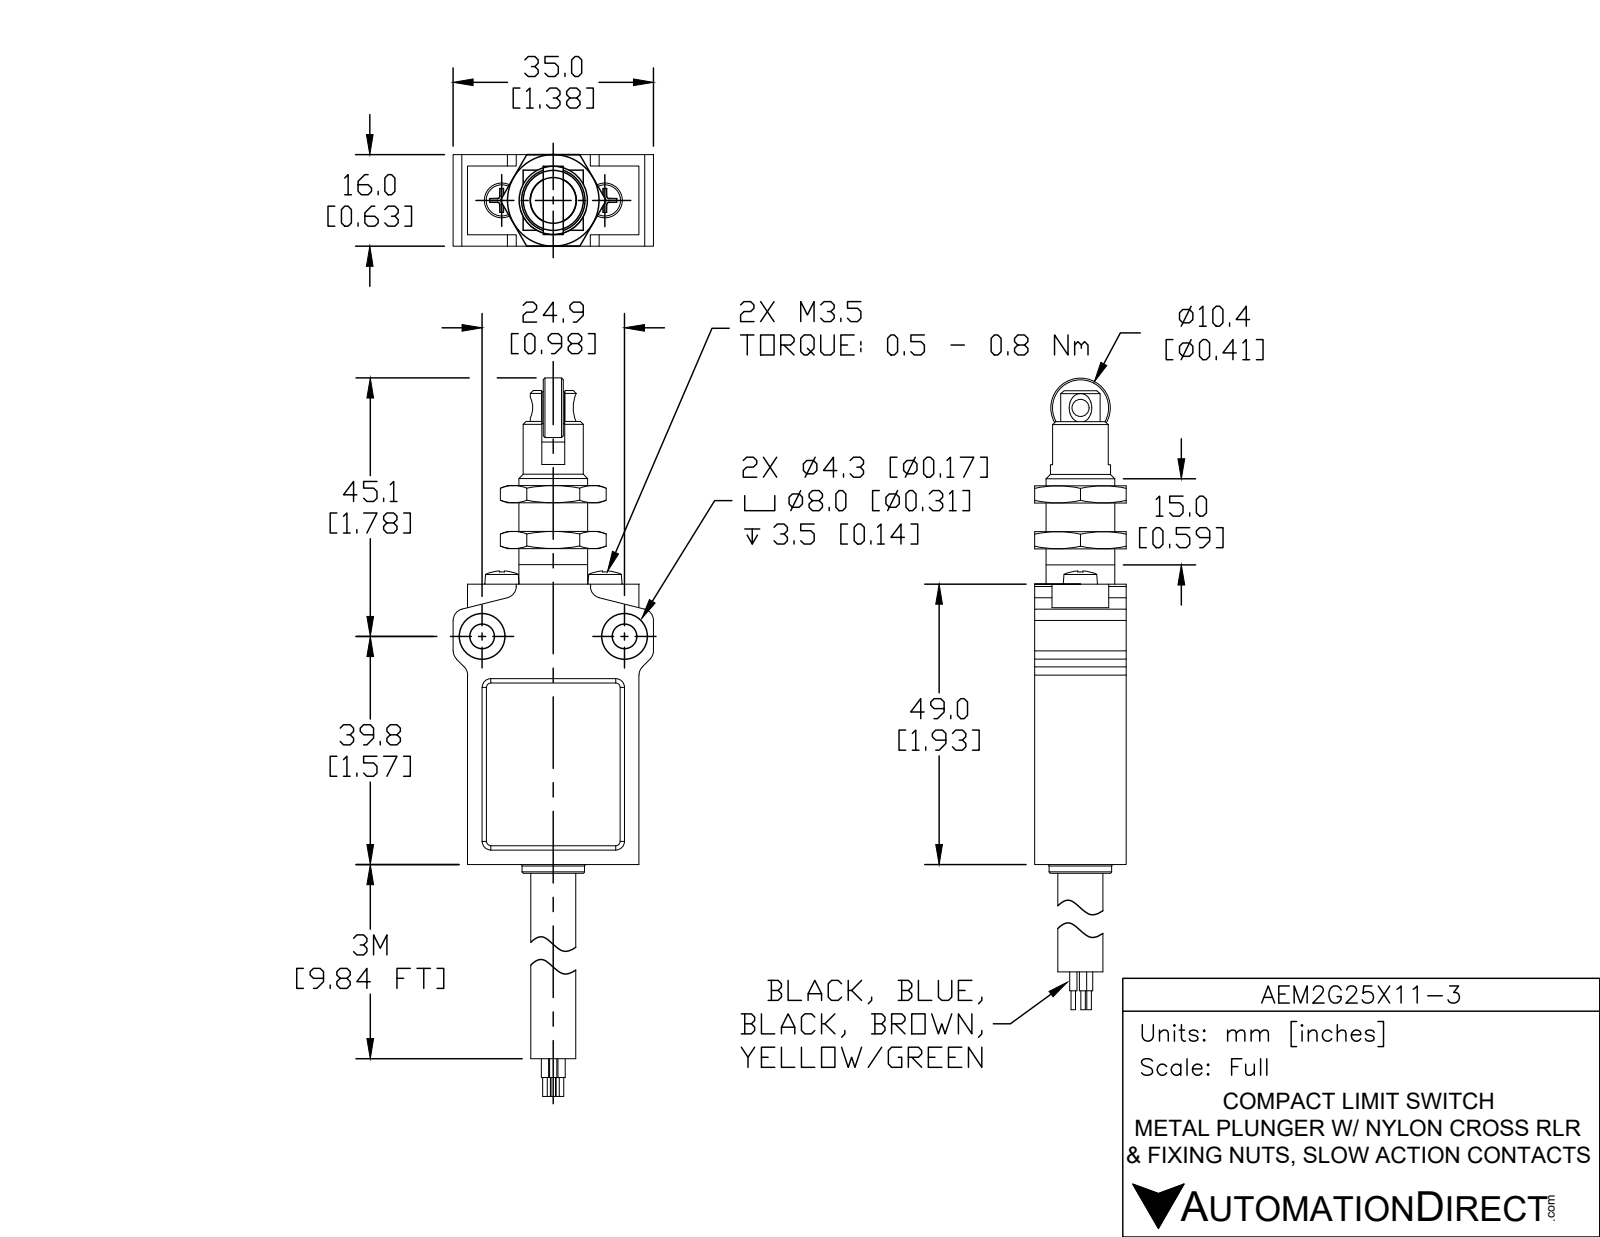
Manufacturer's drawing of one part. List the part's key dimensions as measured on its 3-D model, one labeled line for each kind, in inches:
Part name (STEP PRODUCT): AEM2G25X11-3
STEP written by: SolidWorks 2017 (AUTOMOTIVE_DESIGN)
Units: inches
Bodies: 6 solids, 190 faces (79 planar, 52 cylindrical, 59 other)
Overall size (bounding box): 3.933 × 1.378 × 0.63
Volume: 1.675 in³ · Surface area: 17.53 in²
Round holes (diameter × count): ⌀0.173 ×2, ⌀0.323 ×2, ⌀0.317 ×1, ⌀0.472 ×1
Round bosses / shafts (diameter × count): ⌀0.413 ×1, ⌀0.409 ×1, ⌀0.315 ×1, ⌀0.313 ×1, ⌀0.22 ×1
Partial cylindrical surfaces — rounded edges, fillets, slot ends (radius × count): R0.079 ×8, R0.256 ×1
Main face-to-face distances: 0.63, 1.181, 0.472, 0.118, 1.929, 0.236, 1.74, 0.189, 0.354, 0.157
Hole centre spacings: 0.984
